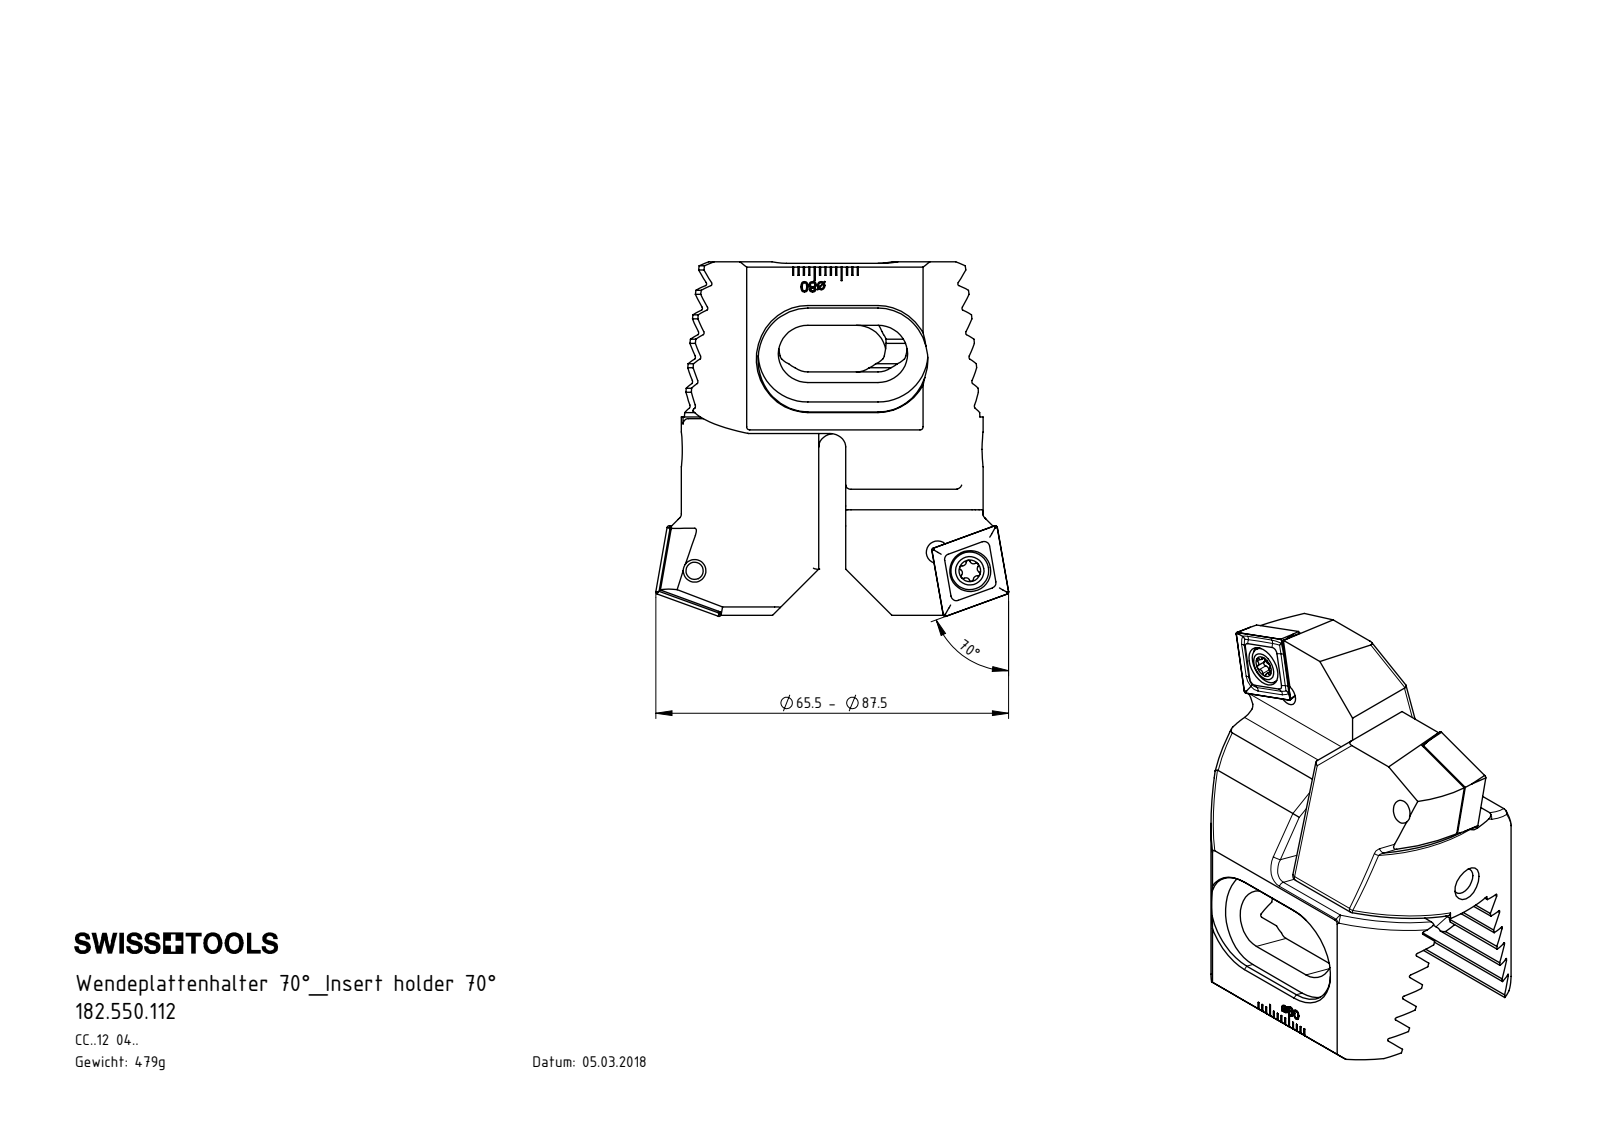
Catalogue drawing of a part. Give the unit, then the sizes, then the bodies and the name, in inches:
Units: inches
Overall size (bounding box): 2.591 × 2.579 × 1.74
Round holes (diameter × count): ⌀0.165 ×4, ⌀0.079 ×2, ⌀0.217 ×2, ⌀0.299 ×2, ⌀0.197 ×1
Round bosses / shafts (diameter × count): ⌀0.276 ×2, ⌀0.197 ×2, ⌀0.236 ×1, ⌀0.157 ×1
Partial cylindrical surfaces — rounded edges, fillets, slot ends (radius × count): R0.039 ×14, R0.013 ×12, R0.015 ×12, R0.027 ×8, R0.118 ×6, R0.027 ×4, R0.217 ×4, R0.364 ×4
Main face-to-face distances: 0.16, 0.32, 0.481, 0.641, 0.801, 0.309, 0.067, 0.858, 0.882, 0.197
Hole centre spacings: 0.271, 0.275, 0.63, 1.781, 1.785, 2.014, 1.217, 1.542
Volume: 3.776 in³ · Surface area: 35.27 in²
Bodies: 8 solids, 692 faces (336 planar, 132 cylindrical, 224 other)
Part name (STEP PRODUCT): Z55-ER3.001.020; WCC-ER2.001.010_A; CCMT120404; Z55-xxx.001.037_C_CC 12 70ø (+1 more)
STEP written by: SolidWorks 2017 (CONFIG_CONTROL_DESIGN)
